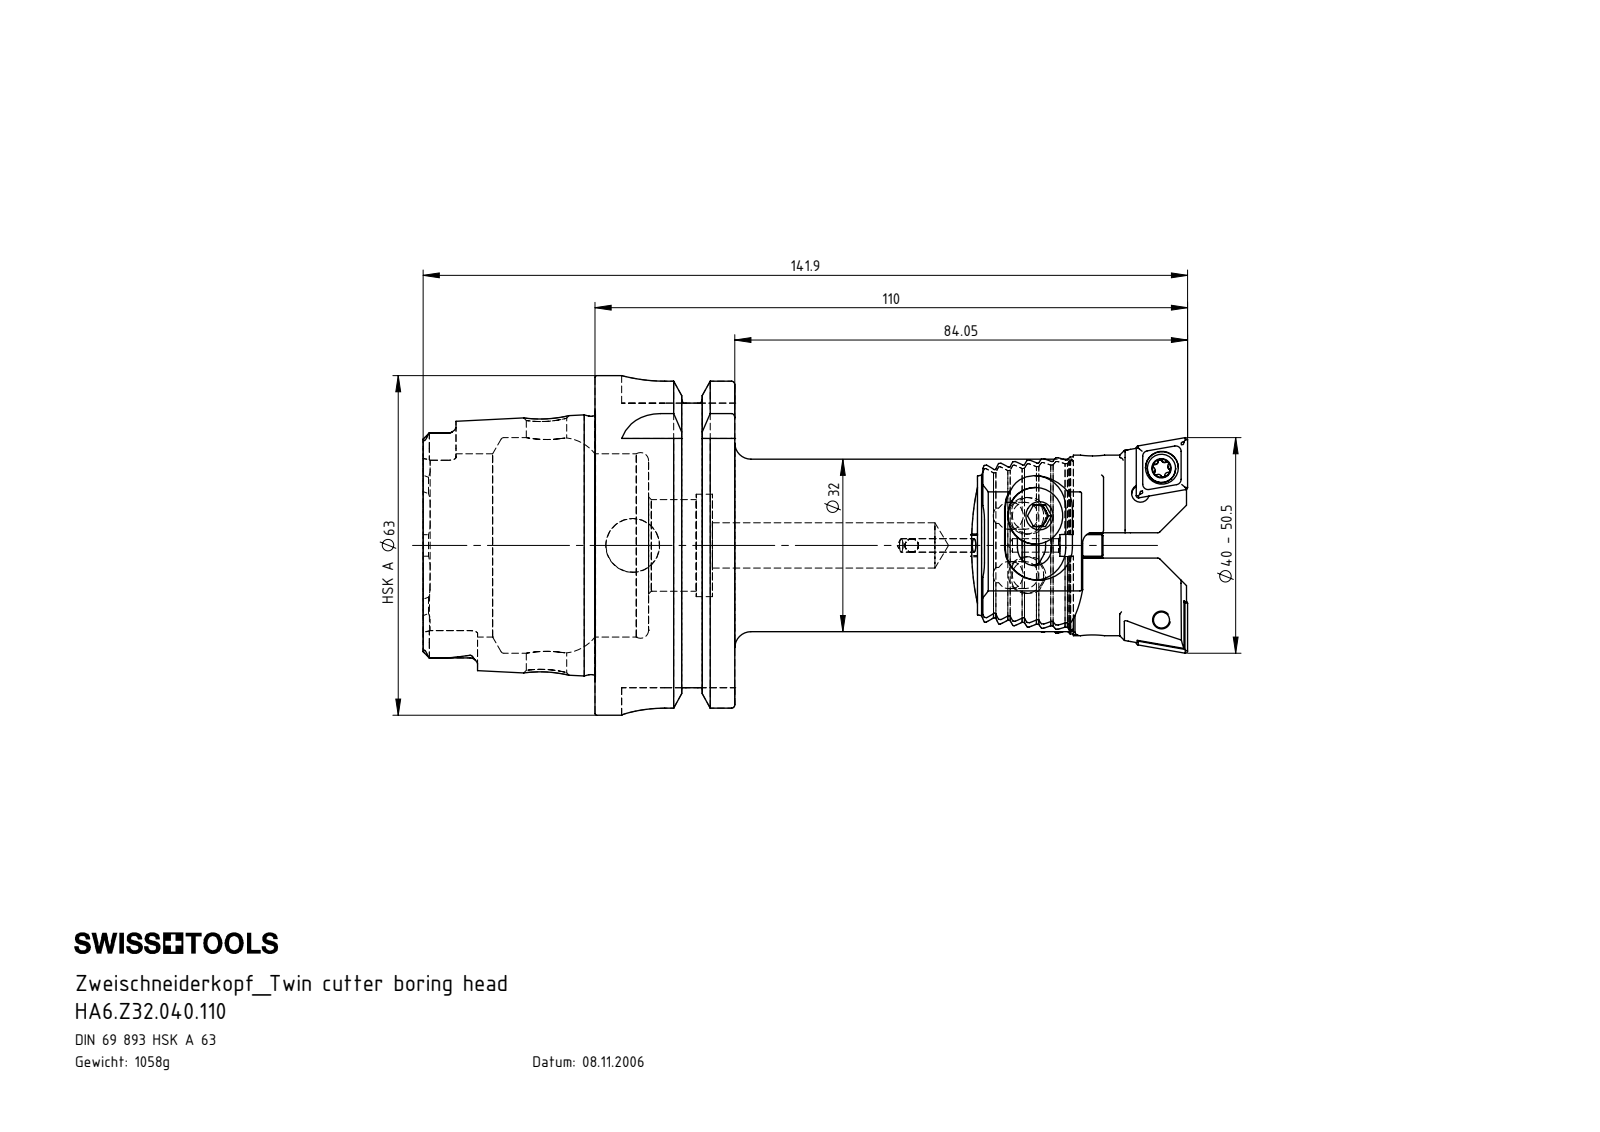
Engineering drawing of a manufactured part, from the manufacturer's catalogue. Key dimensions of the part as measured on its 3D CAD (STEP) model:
Part name (STEP PRODUCT): HA6-Z32.K23.110_A_Fertigbearbeitung; Z32-ER1.003.016_A_gespannt; Z32-ER1.001.016; Z32-ER1.002.016_A (+2 more)
STEP written by: SolidWorks 2017 (AUTOMOTIVE_DESIGN)
Units: millimetres
Bodies: 6 solids, 350 faces (188 planar, 84 cylindrical, 78 other)
Overall size (bounding box): 126.2 × 63 × 63
Volume: 122 903 mm³ · Surface area: 31 831 mm²
Round holes (diameter × count): ⌀2.5 ×4, ⌀5 ×2, ⌀6.4 ×2, ⌀6.8 ×2, ⌀2 ×1, ⌀7.5 ×1, ⌀8.4 ×1, ⌀10 ×1, ⌀17 ×1, ⌀19 ×1, ⌀34 ×1, ⌀40 ×1
Round bosses / shafts (diameter × count): ⌀10.5 ×2, ⌀10.2 ×2, ⌀6 ×2, ⌀63 ×1, ⌀54.95 ×1, ⌀47.94 ×1, ⌀32 ×1, ⌀4 ×1
Partial cylindrical surfaces — rounded edges, fillets, slot ends (radius × count): R0.2 ×14, R1.4 ×6, R2.88 ×4, R8 ×4, R220 ×2
Main face-to-face distances: 25.95, 2.38, 16, 9.95, 4.76, 31.9, 41.85, 57.85, 7.14, 7.15
Hole centre spacings: 51.8
